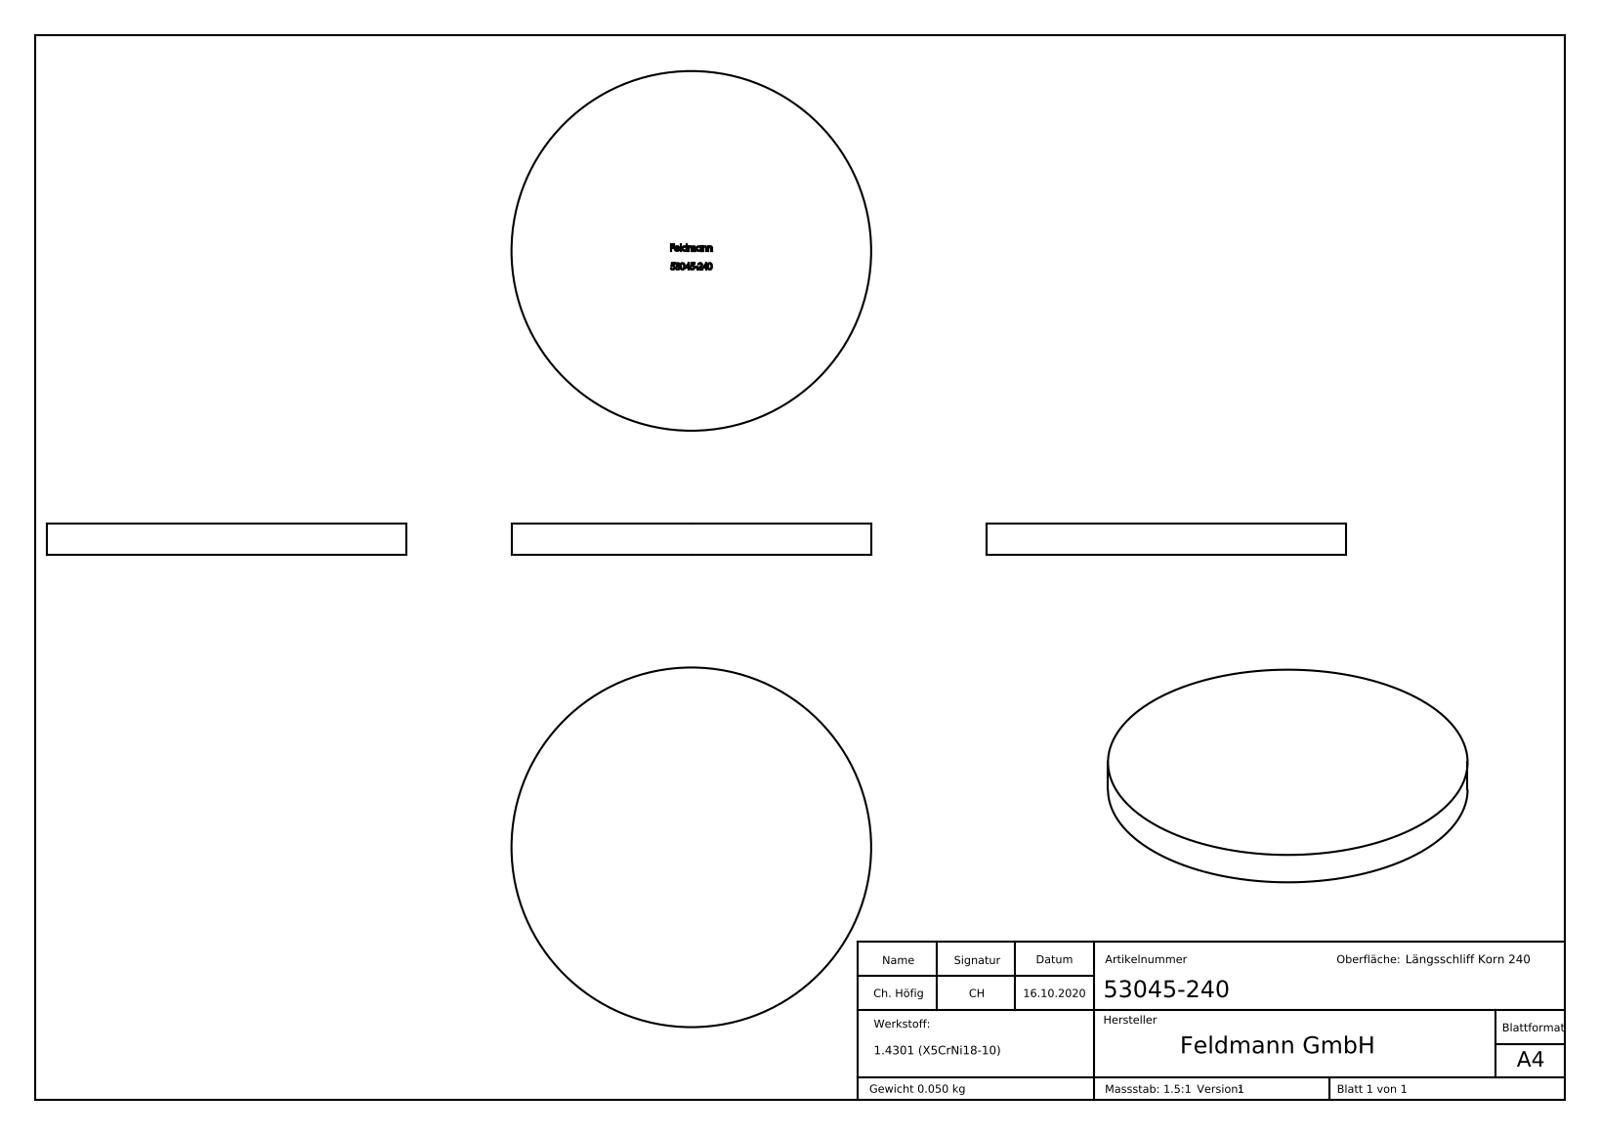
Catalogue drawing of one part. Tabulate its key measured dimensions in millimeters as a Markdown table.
| quantity | value |
| --- | --- |
| part name | 53045-240 |
| STEP written by | SolidWorks 2018 (CONFIG_CONTROL_DESIGN) |
| units | millimeters |
| bodies | 1 solid, 235 faces (131 planar, 2 cylindrical, 102 other) |
| overall size | 45 × 45 × 4 |
| volume | 6 362 mm³ |
| surface area | 3 752 mm² |
| round bosses / shafts (diameter × count) | 45 × 1 |
| main face-to-face distances | 4, 3.9, 2.2, 1.78, 2.18, 0.83, 2.41, 0.79, 2.25, 2.4 |
